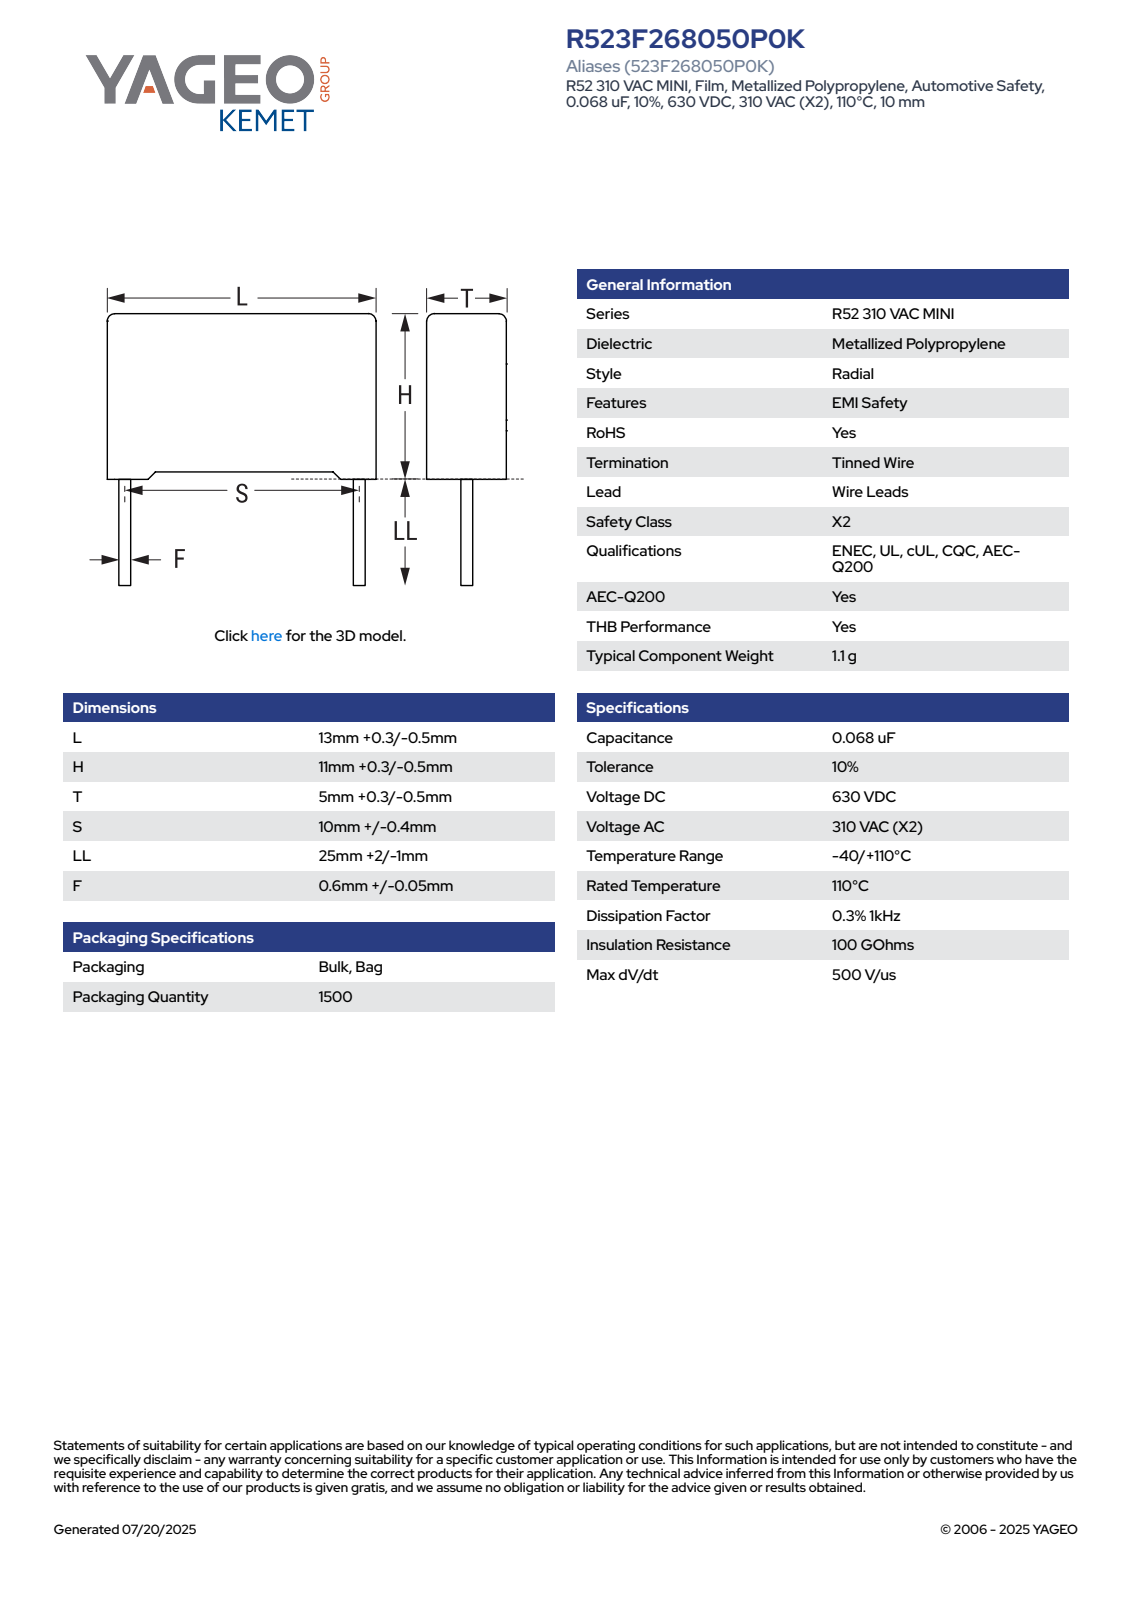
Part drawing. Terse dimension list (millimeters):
name: CFR_RB2_13X11X5_L13.3H11.3T5.3S10LL27F0.65
written by: SolidWorks 2021 (AUTOMOTIVE_DESIGN)
unit: mm
bodies: 4 solids, 85 faces (77 planar, 8 cylindrical, 0 other)
size: 38.3 × 13.3 × 5.3
volume: 770 mm³; area: 695 mm²
bosses: 2× ⌀0.65
rounds: 4× R0.5
face distances: 5.3, 13.3, 10.55, 0.44, 4.86, 0.75, 11.3, 4.42, 12.86, 0.36
